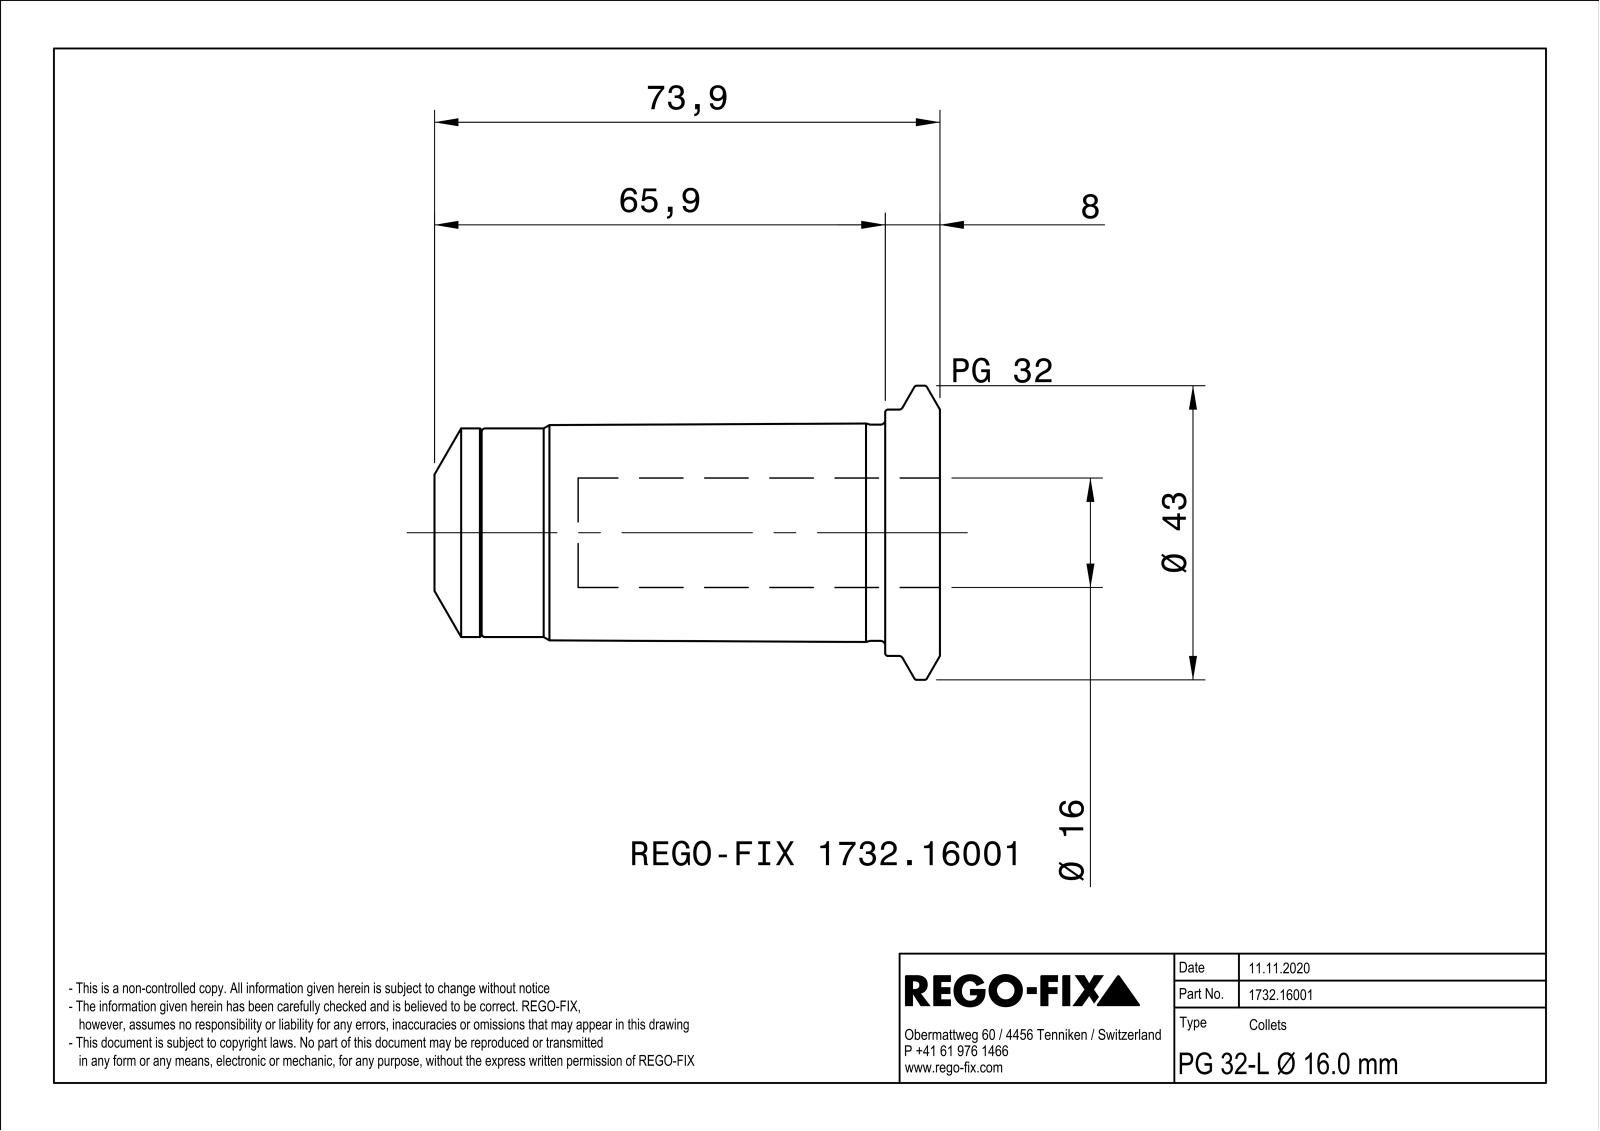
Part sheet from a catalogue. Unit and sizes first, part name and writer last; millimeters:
Units: millimetres
Overall size (bounding box): 73.9 × 43 × 42.99
Round holes (diameter × count): ⌀5 ×1, ⌀16 ×1, ⌀25.5 ×1, ⌀26.92 ×1, ⌀28.5 ×1
Round bosses / shafts (diameter × count): ⌀43 ×1, ⌀36 ×1, ⌀31.6 ×1, ⌀30.5 ×1, ⌀26.7 ×1
Partial cylindrical surfaces — rounded edges, fillets, slot ends (radius × count): R2.5 ×3
Main face-to-face distances: 1, 73.9, 8, 59, 65.9, 58, 50, 15.9, 51, 14.9
Volume: 38 268 mm³ · Surface area: 16 747 mm²
Bodies: 1 solid, 94 faces (29 planar, 21 cylindrical, 44 other)
Part name (STEP PRODUCT): NOCUT
STEP written by: SIEMENS PLM Software Solid Edge ST10 (AUTOMOTIVE_DESIGN)
